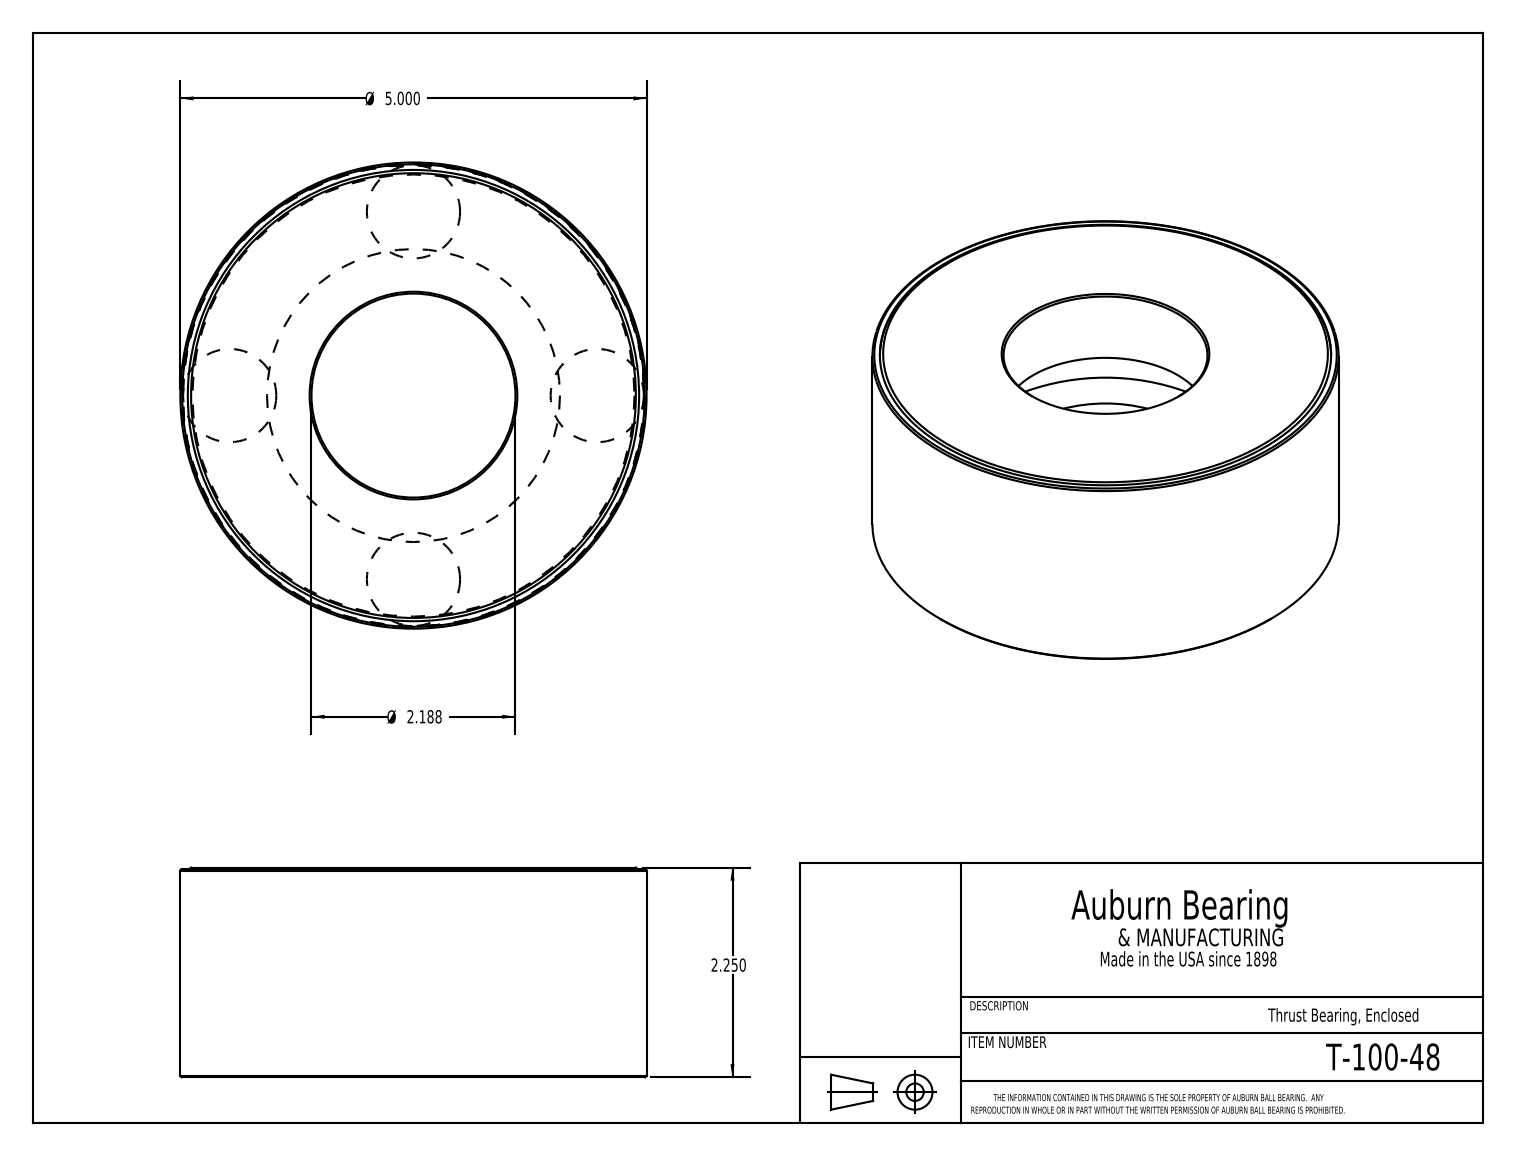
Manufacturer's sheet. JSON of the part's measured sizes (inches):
{"part_name": "T-100-48", "step_written_by": "SolidWorks 2016 (CONFIG_CONTROL_DESIGN)", "units": "inches", "bodies": {"solids": 6, "faces": 28, "planar": 9, "cylindrical": 7, "other": 12}, "overall_size": [5, 5, 2.25], "volume_in3": 25.57, "surface_area_in2": 160.3, "round_holes": [[2.187, 1], [4.84, 1], [4.96, 1]], "round_bosses_or_shafts": [[5, 1], [4.946, 1]], "face_to_face_distances": [2.25, 0.825, 1.425, 1.425, 0.6, 0.825, 2.235, 1.41, 0.81, 0.015]}
